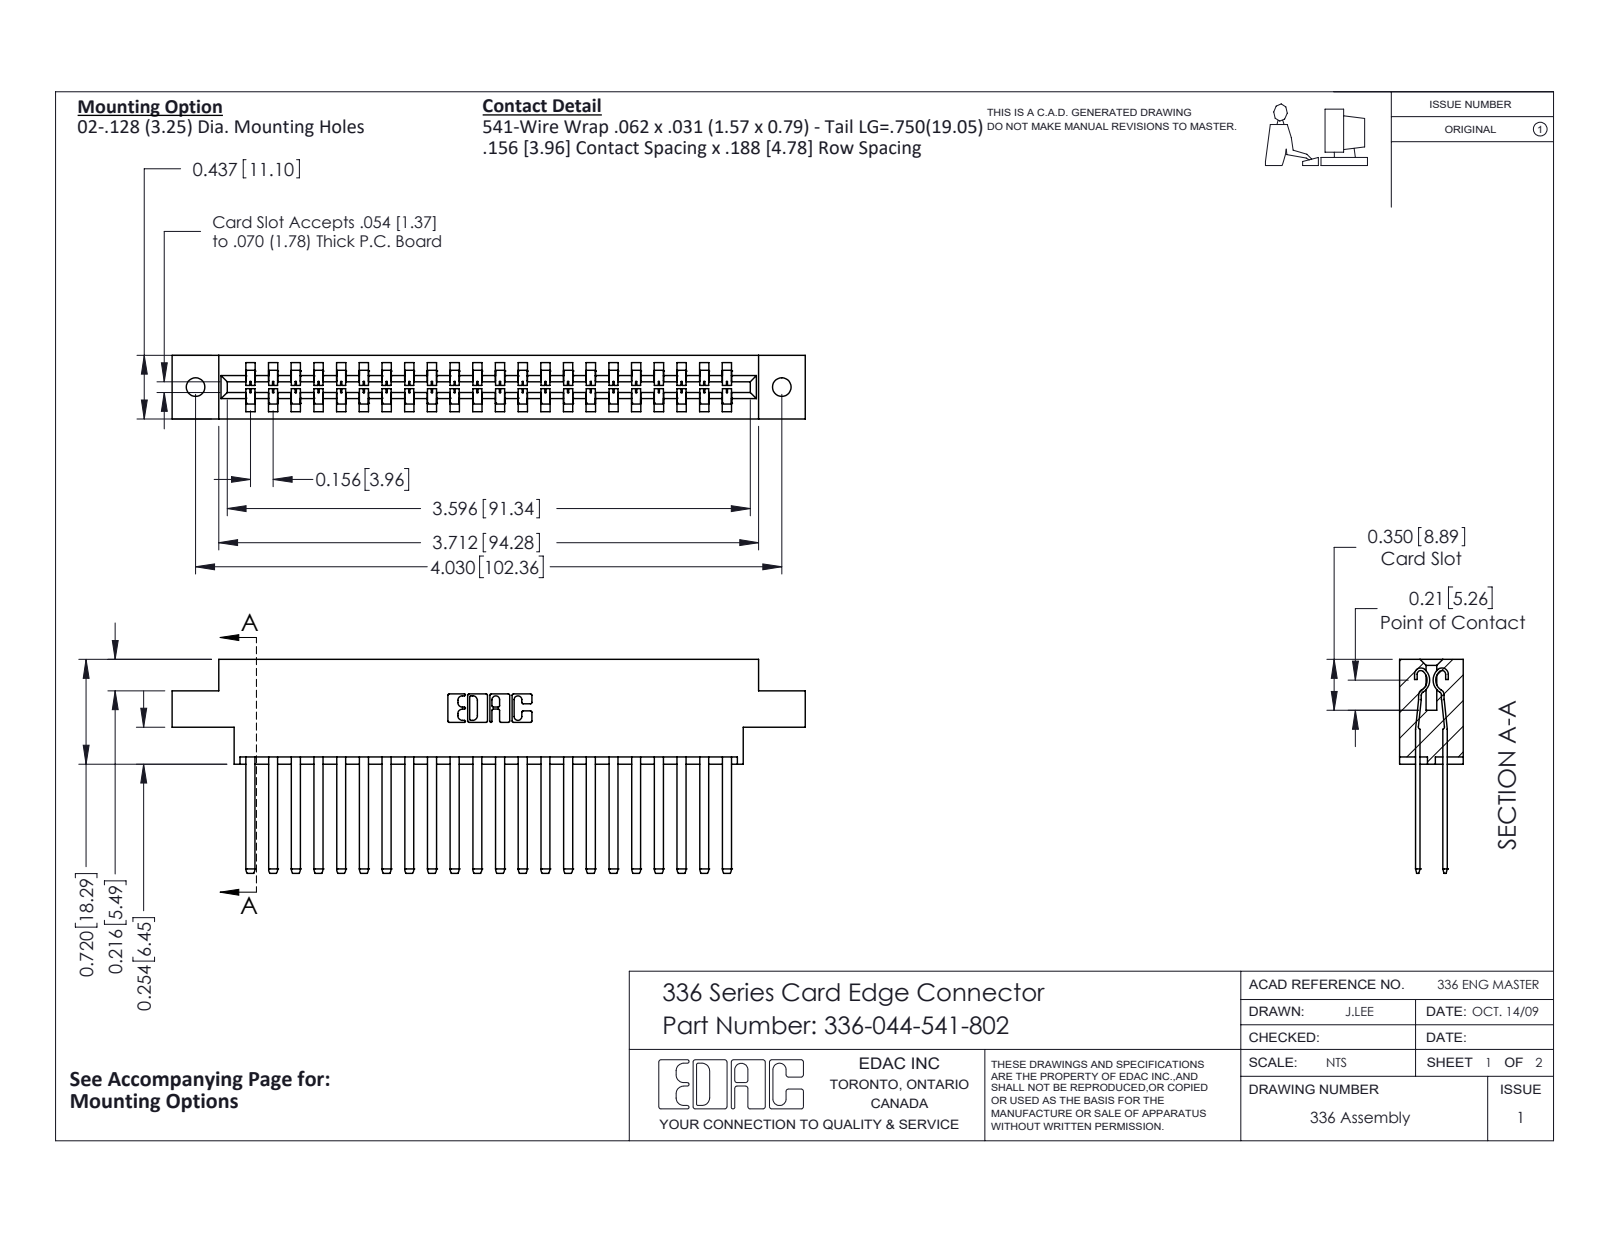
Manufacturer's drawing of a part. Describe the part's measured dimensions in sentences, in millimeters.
The part is named "336-290-001_336-290-541; 336-044-541-802; 336 Part_Offset - .128 Dia". Its 3-D file was written by "SolidWorks 2020 (CONFIG_CONTROL_DESIGN)". It is 45 solids with 1966 faces: 1218 planar, 748 cylindrical and 0 other. Overall it measures 110.6 by 37.3 by 11.1 millimeters. Its volume is 16 200 cubic millimeters and its surface area 20 310 square millimeters. Round holes: 2 of diameter 3.3. Partial cylindrical surfaces (rounded edges, fillets, slot ends): 88 of radius 0.1, 44 of radius 1.4, 22 of radius 0.3, 6 of radius 0.2, 6 of radius 0.8, 4 of radius 0.6, 4 of radius 1, 3 of radius 0.7. The main face-to-face distances are 4.8, 8.3, 3.6, 7.5, 2.8, 0.8, 11.1, 0.8, 4, 4.6. The hole center spacings are 102.4.
